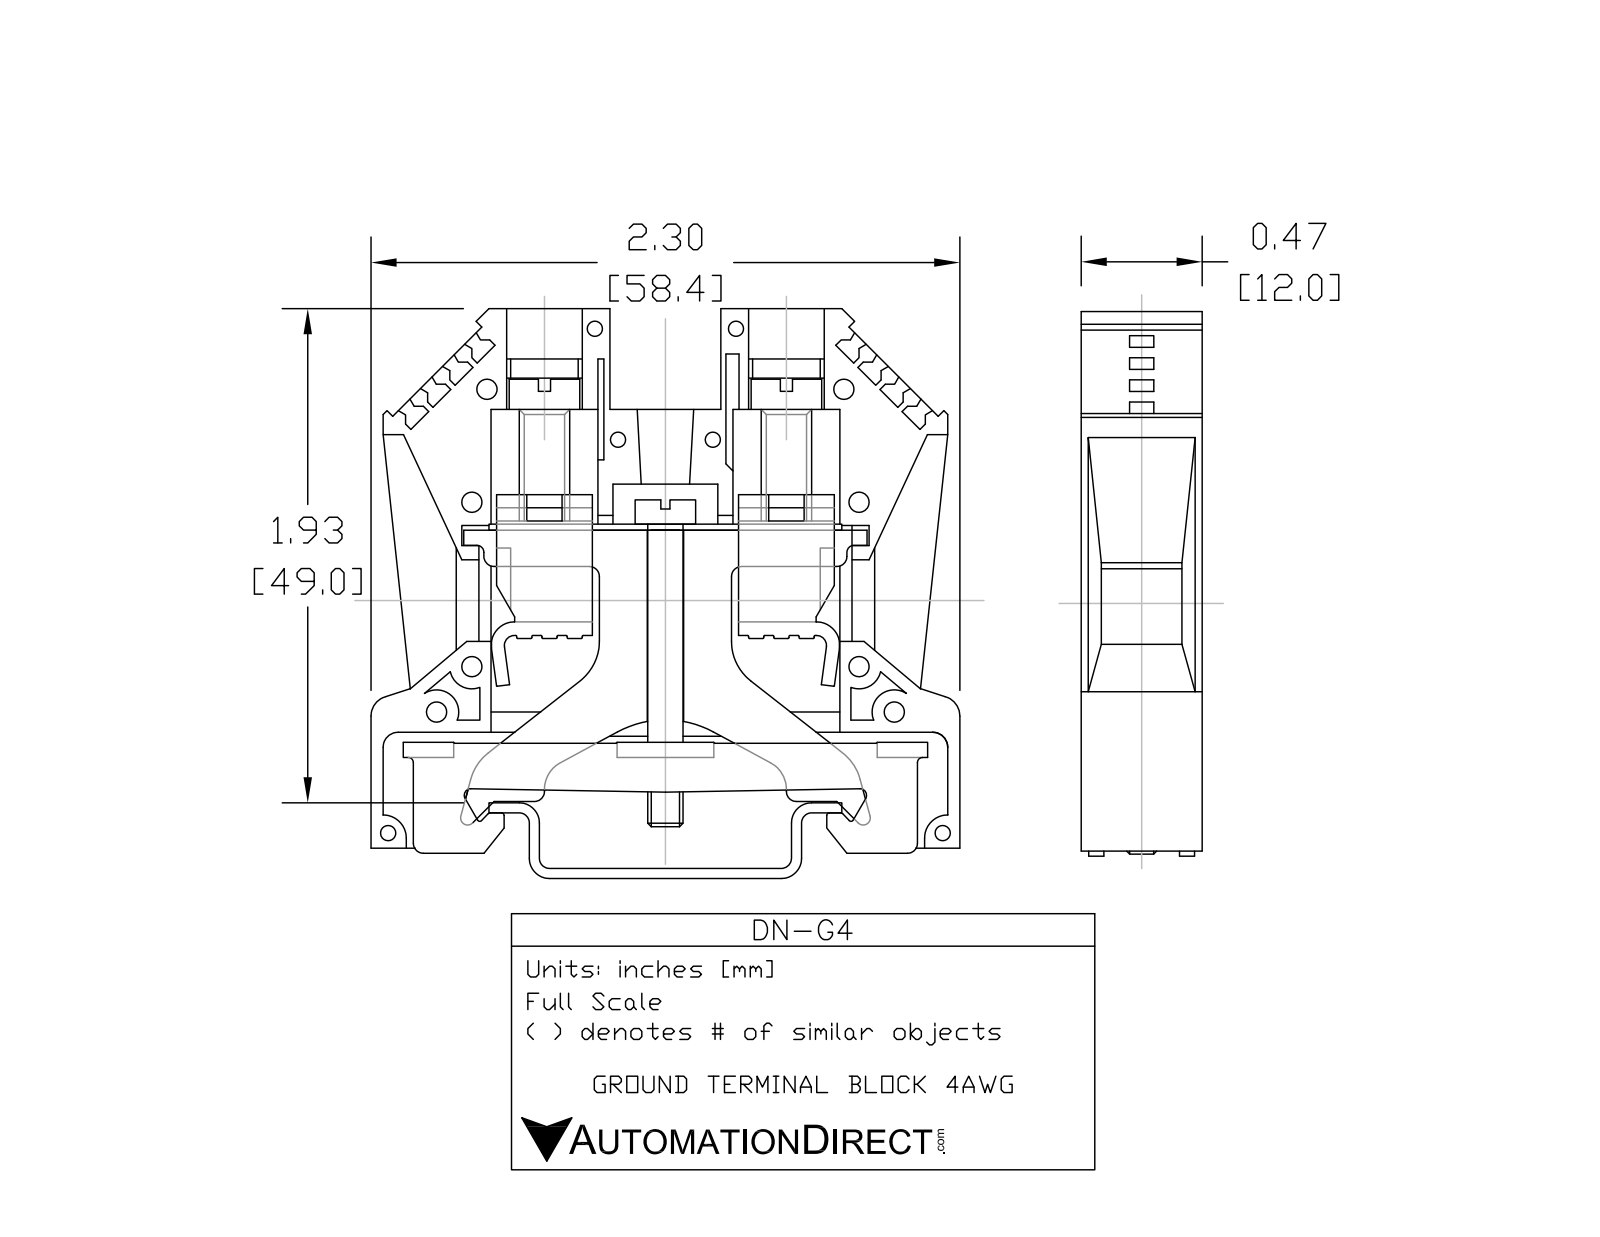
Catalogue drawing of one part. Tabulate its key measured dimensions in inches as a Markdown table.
| quantity | value |
| --- | --- |
| part name | 20553; 43451_DN-G4 |
| STEP written by | SolidWorks 2013 (AUTOMOTIVE_DESIGN) |
| units | inches |
| bodies | 1 solid, 174 faces (148 planar, 26 cylindrical, 0 other) |
| overall size | 2.299 × 2.106 × 0.472 |
| volume | 1.828 in³ |
| surface area | 13.57 in² |
| round holes (diameter × count) | 0.307 × 2, 0.22 × 1 |
| round bosses / shafts (diameter × count) | 0.264 × 2, 0.189 × 1 |
| partial cylindrical surfaces (radius × count) | 0.01 × 6, 0.079 × 2 |
| main face-to-face distances | 0.472, 0.933, 1.366, 1.909, 0.197, 2.106, 2.299, 1.319, 0.433, 0.394 |
| hole center spacings | 0.472, 0.945 |
